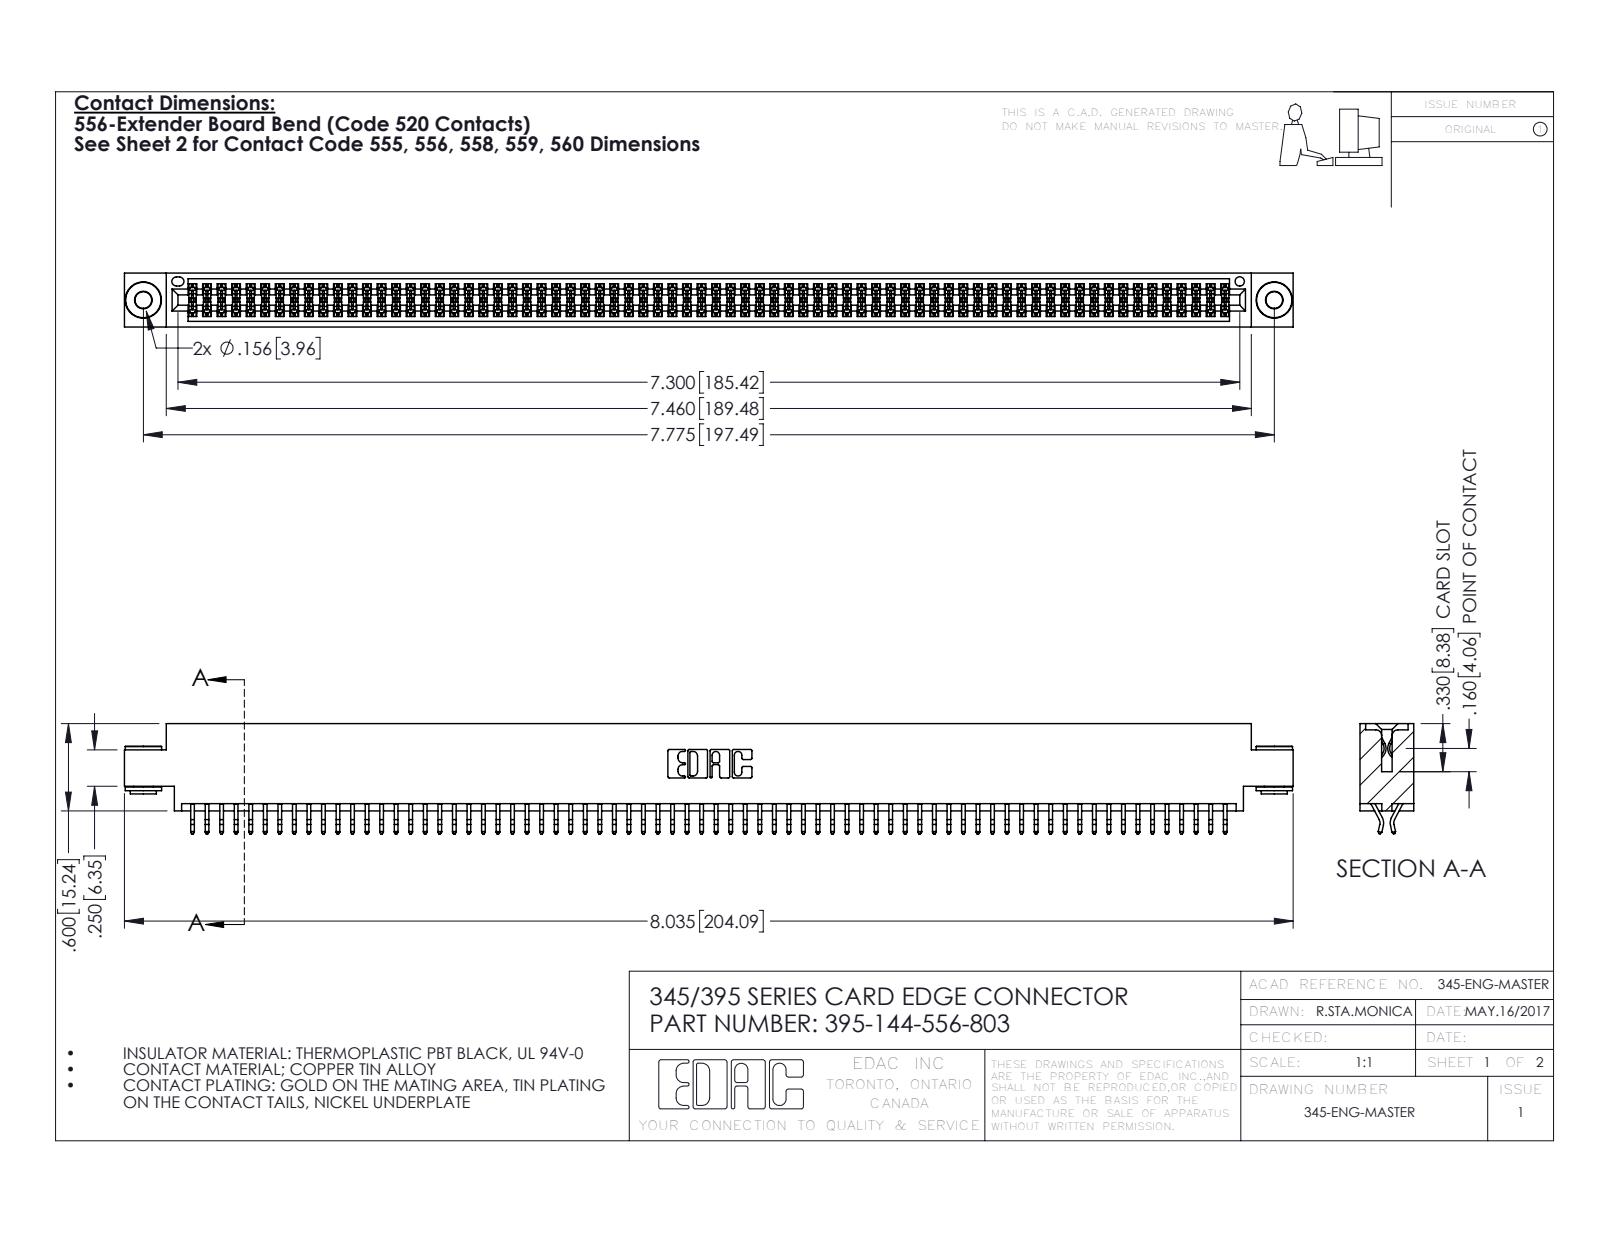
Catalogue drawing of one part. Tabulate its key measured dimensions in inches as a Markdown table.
| quantity | value |
| --- | --- |
| part name | 395-144-556-803; 345-250-002_345-250-002-102; 345 Part_0.170 Offset - 0.156 Dia-TH; 345-292-001_556 Tail |
| STEP written by | SolidWorks 2016 (CONFIG_CONTROL_DESIGN) |
| units | inches |
| bodies | 147 solids, 8232 faces (5422 planar, 2802 cylindrical, 8 other) |
| overall size | 8.035 × 0.757 × 0.37 |
| volume | 1.221 in³ |
| surface area | 47.08 in² |
| round holes (diameter × count) | 0.116 × 2, 0.156 × 2, 0.064 × 1 |
| round bosses / shafts (diameter × count) | 0.25 × 2, 0.18 × 2, 0.136 × 2 |
| partial cylindrical surfaces (radius × count) | 0.006 × 216, 0.01 × 22, 0.007 × 6, 0.031 × 6, 0.026 × 3, 0.01 × 2, 0.014 × 2, 0.019 × 2 |
| main face-to-face distances | 0.072, 0.298, 0.37, 0.2, 0.025, 0.098, 0.272, 0.225, 0.175, 0.149 |
| hole center spacings | 0.27, 7.539, 7.775 |
